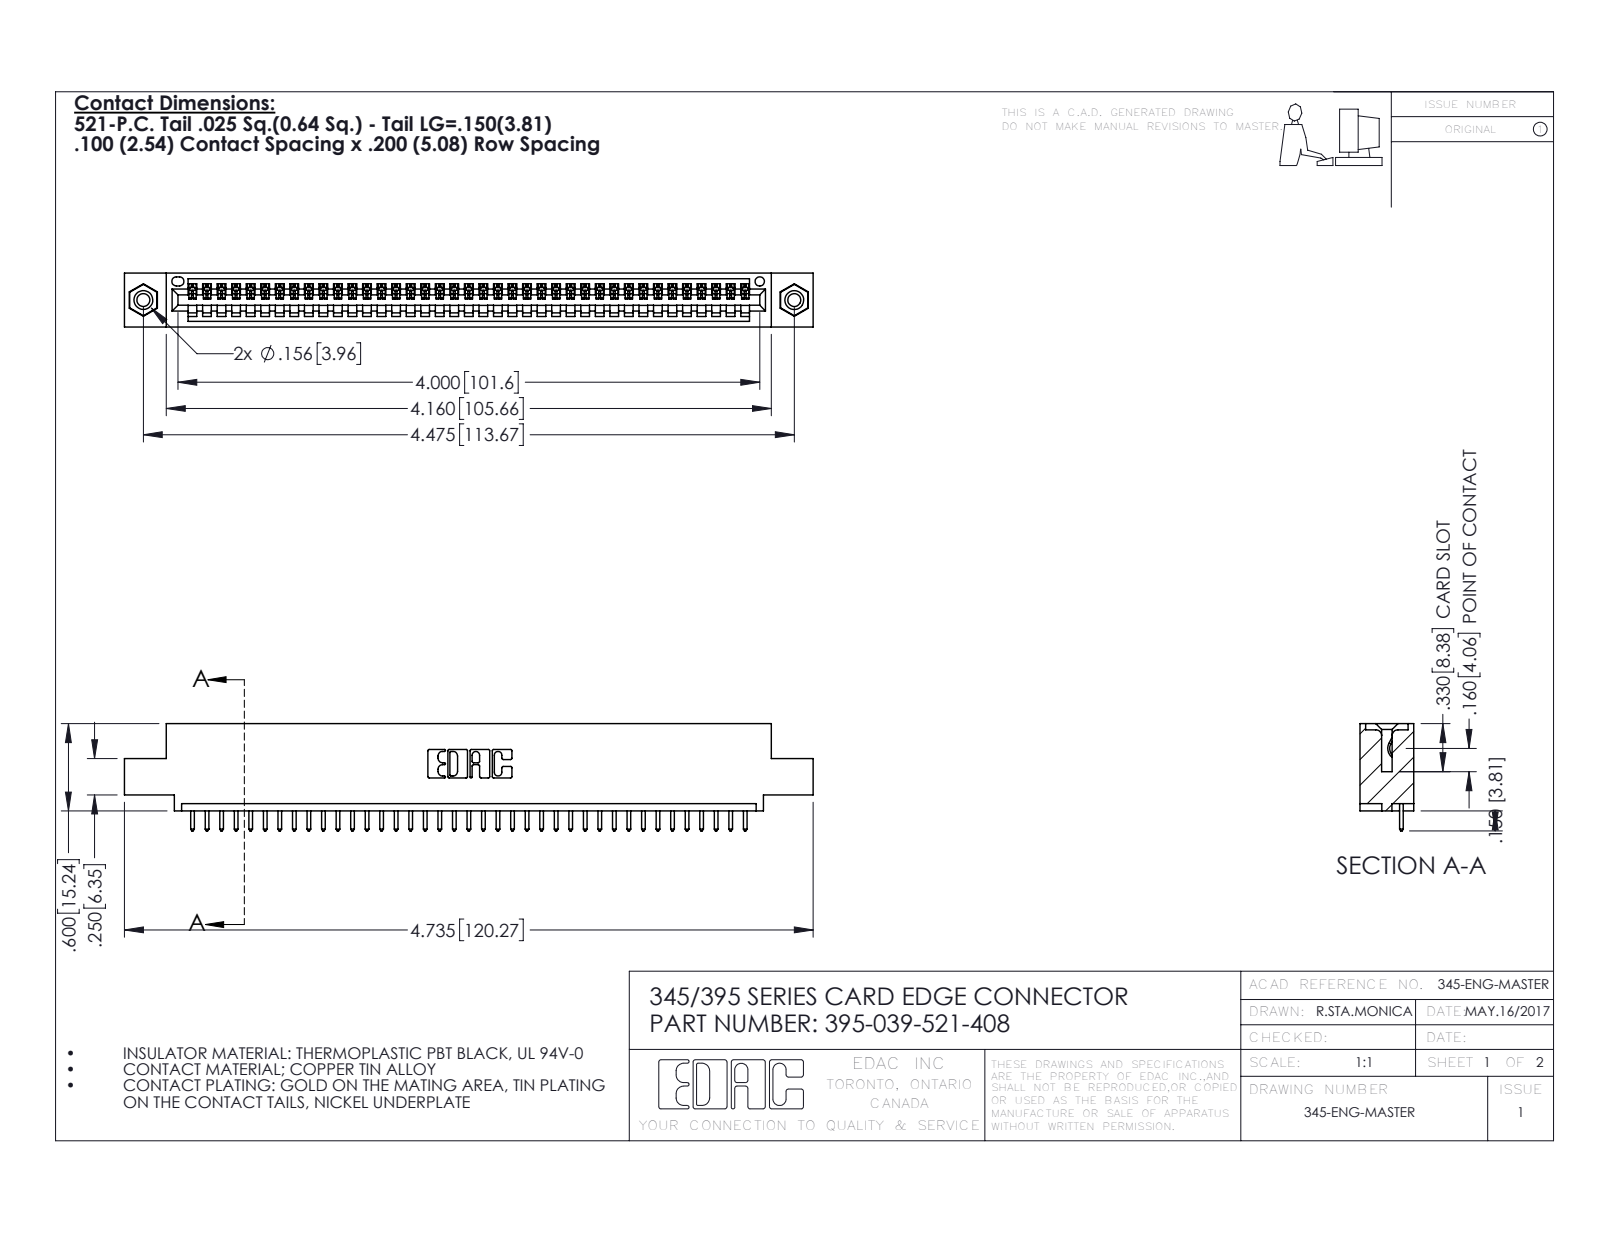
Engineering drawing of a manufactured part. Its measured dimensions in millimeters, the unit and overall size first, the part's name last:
Units: millimetres
Overall size (bounding box): 120.3 × 18.7 × 9.4
Round holes (diameter × count): ⌀2.3 ×2, ⌀3.2 ×2, ⌀4 ×2, ⌀1.6 ×1
Round bosses / shafts (diameter × count): ⌀3.9 ×2
Partial cylindrical surfaces — rounded edges, fillets, slot ends (radius × count): R0.2 ×78, R0.3 ×78, R0.3 ×22, R0.2 ×6, R0.8 ×6, R0.7 ×3, R0.8 ×2, R1 ×2
Main face-to-face distances: 1.8, 7.6, 9.4, 5.1, 2.5, 6.9, 0.6, 5.7, 3.8, 1.8
Hole centre spacings: 6.9, 107.7, 113.7
Volume: 11 200 mm³ · Surface area: 14 520 mm²
Bodies: 42 solids, 2452 faces (1676 planar, 760 cylindrical, 16 other)
Part name (STEP PRODUCT): 395-039-521-408; 345 Part_0.110 Offset - 0.156 Dia-TI; 345-250-001_345-250-003-102; 345-292-001_345-293-121
STEP written by: SolidWorks 2016 (CONFIG_CONTROL_DESIGN)
